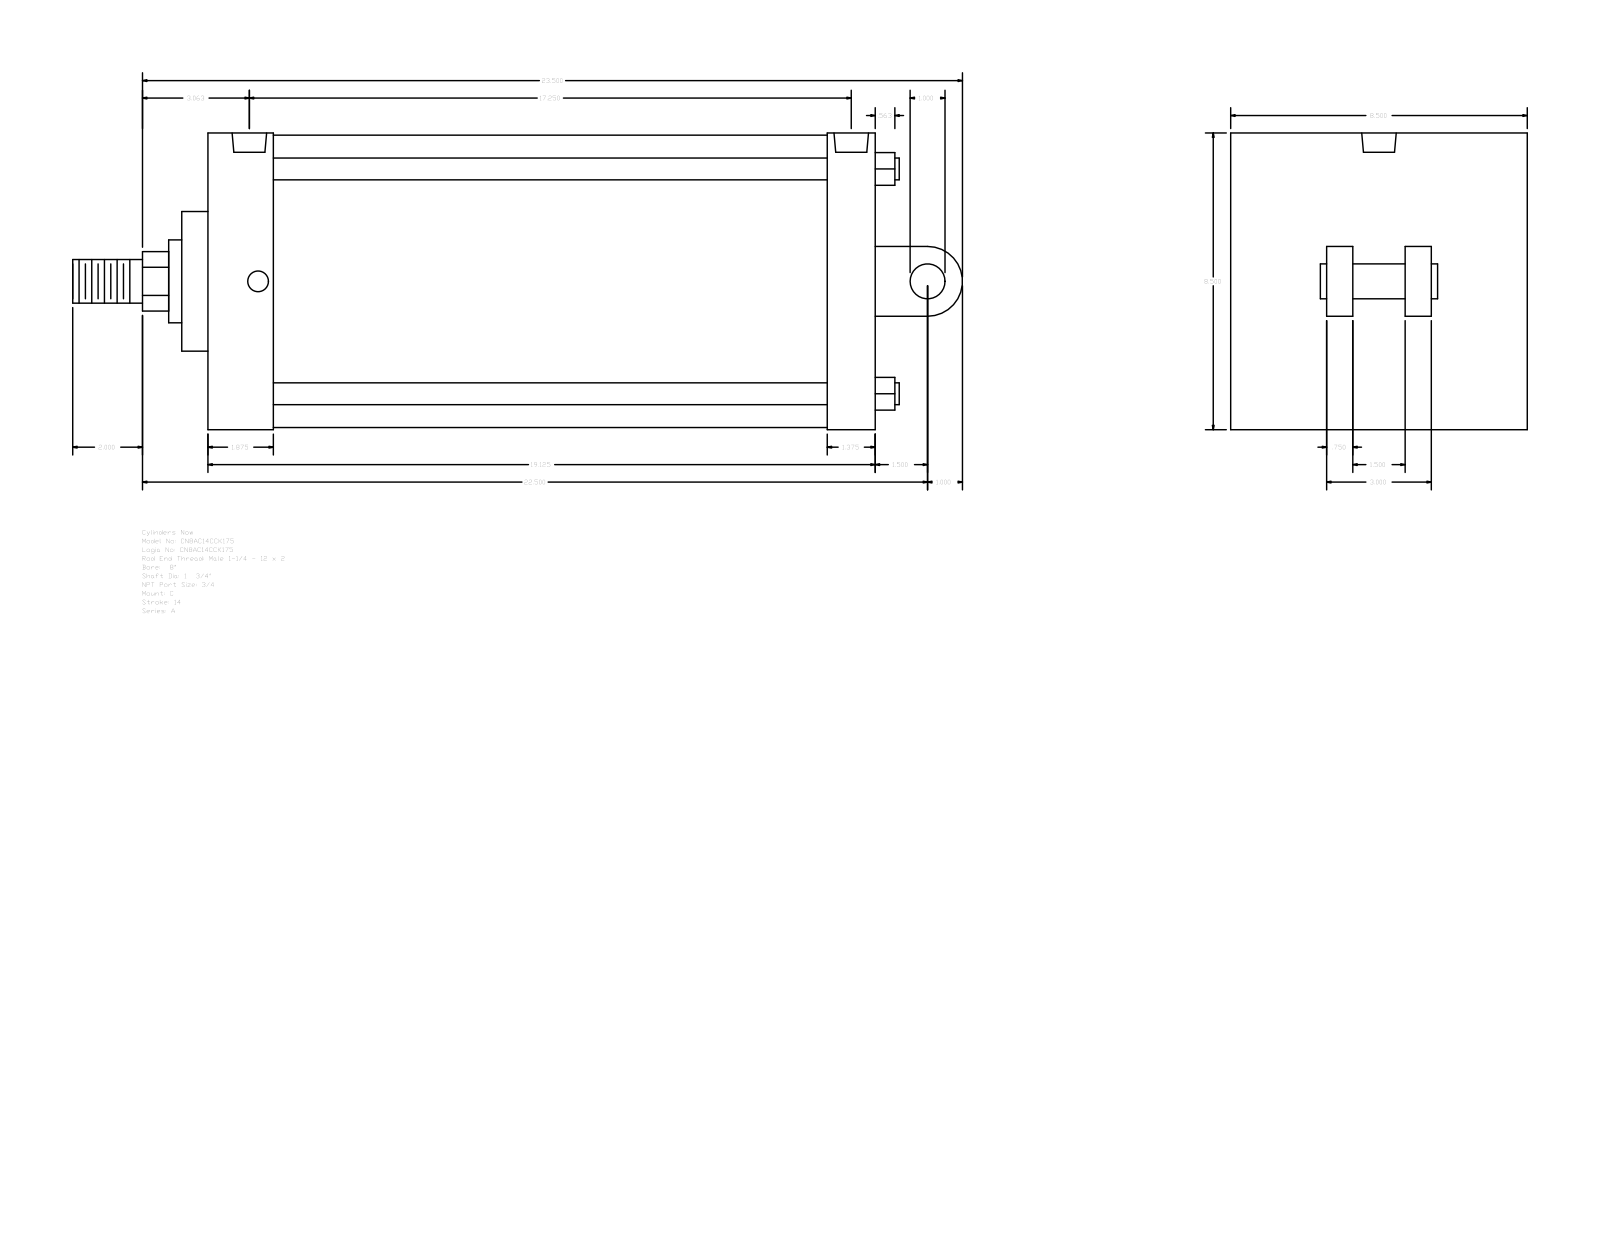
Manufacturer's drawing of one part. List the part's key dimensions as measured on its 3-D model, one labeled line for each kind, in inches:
Part name (STEP PRODUCT): A_C__0800_1.75
STEP written by: GSSL Pune (CONFIG_CONTROL_DESIGN)
Units: inches
Bodies: 0 solids, 104 faces (75 planar, 29 cylindrical, 0 other)
Overall size (bounding box): 25.5 × 8.5 × 8.5
Round holes (diameter × count): ⌀0.594 ×4, ⌀0.989 ×2
Round bosses / shafts (diameter × count): ⌀0.625 ×4, ⌀8.375 ×1, ⌀2.375 ×1, ⌀1.75 ×1, ⌀1.25 ×1, ⌀1 ×1
Partial cylindrical surfaces — rounded edges, fillets, slot ends (radius × count): R0.852 ×1, R1 ×1
Main face-to-face distances: 19.125, 8.5, 0.75, 2.25, 1.875, 17.25, 17.75, 15.875, 1.375, 2.75
Hole centre spacings: 0.25, 16.75, 17, 17.25
